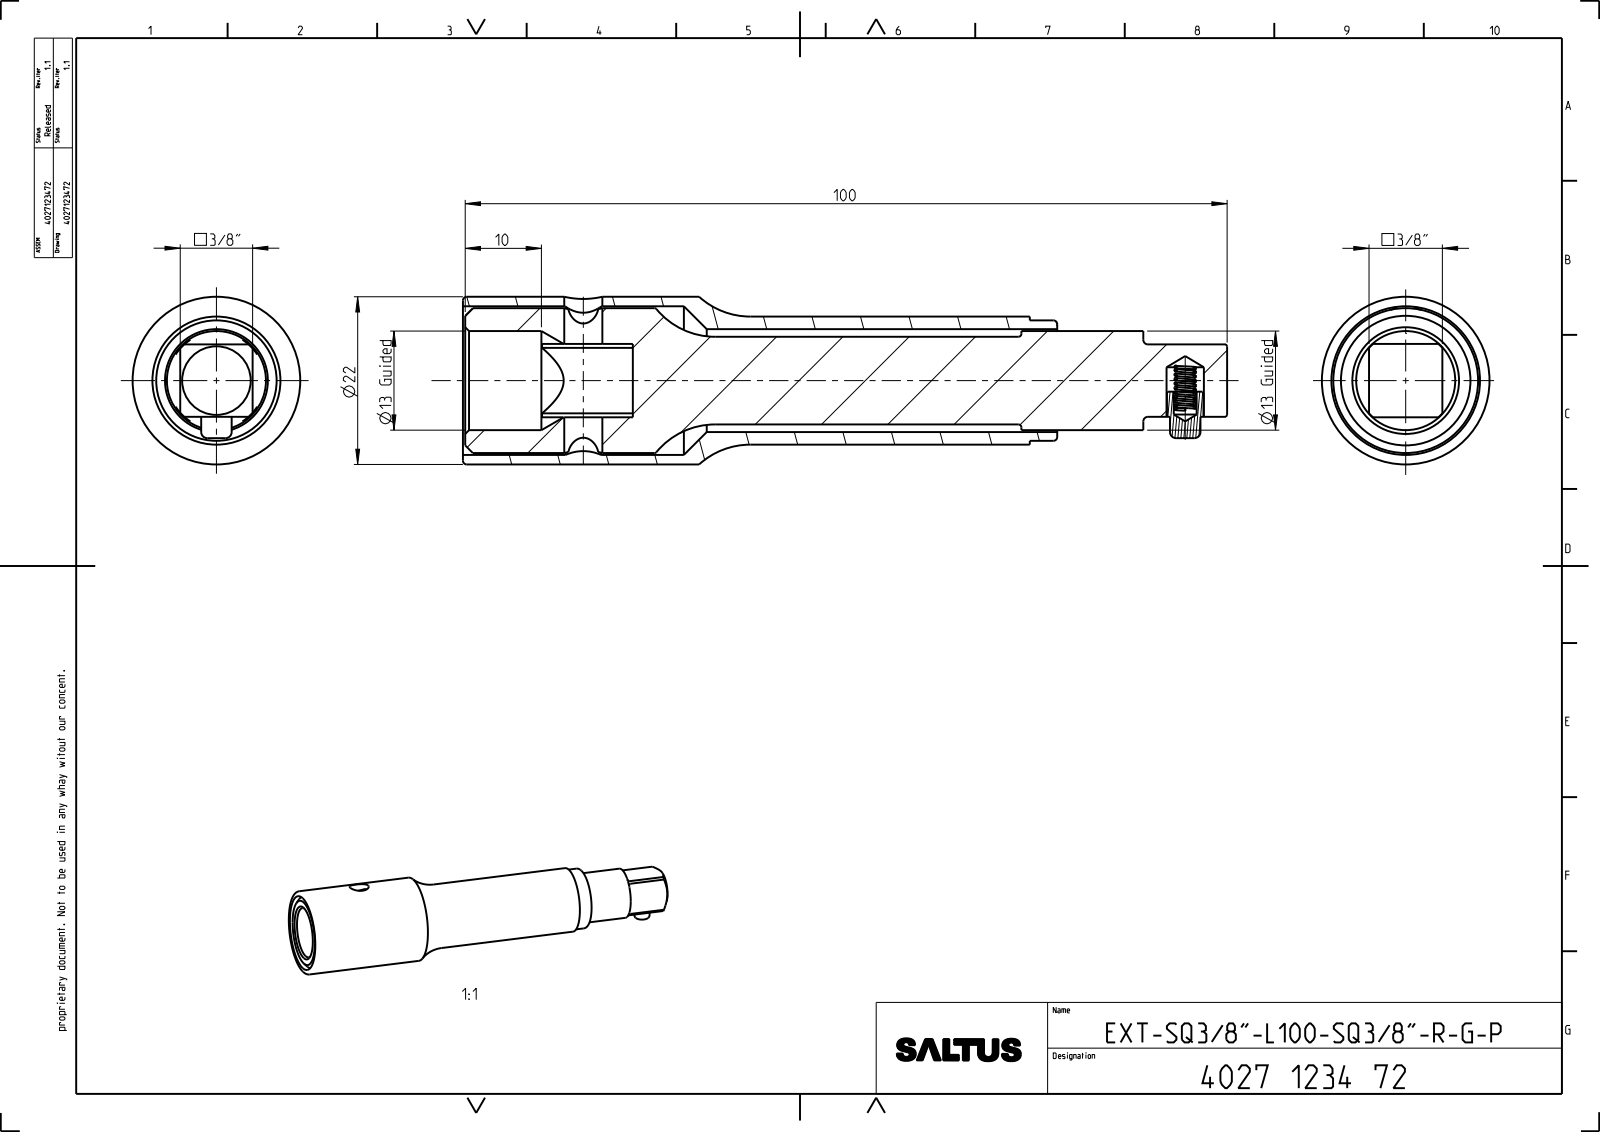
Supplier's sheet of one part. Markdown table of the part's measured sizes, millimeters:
| quantity | value |
| --- | --- |
| part name | 4027021486; 4027299506; 4027907143_OLD; IMPORTIERT1 (+3 more) |
| STEP written by | CREO PARAMETRIC BY PTC INC, 2022414 (CONFIG_CONTROL_DESIGN) |
| units | millimeters |
| bodies | 5 solids, 110 faces (23 planar, 50 cylindrical, 37 other) |
| overall size | 100.3 × 22 × 22 |
| volume | 19 183 mm³ |
| surface area | 14 764 mm² |
| round holes (diameter × count) | 3 × 1, 4.9 × 1, 5 × 1, 13 × 1, 13.5 × 1, 19.5 × 1 |
| round bosses / shafts (diameter × count) | 22 × 1, 19 × 1, 16.8 × 1, 15.8 × 1, 11.5 × 1, 4.8 × 1, 4 × 1 |
| partial cylindrical surfaces (radius × count) | 0.6 × 4, 6.35 × 1, 6.45 × 1 |
| main face-to-face distances | 9.56, 9.5, 9.62, 78, 22.3, 22, 100, 100.3, 55.7, 77.7 |
| hole center spacings | 79 |
